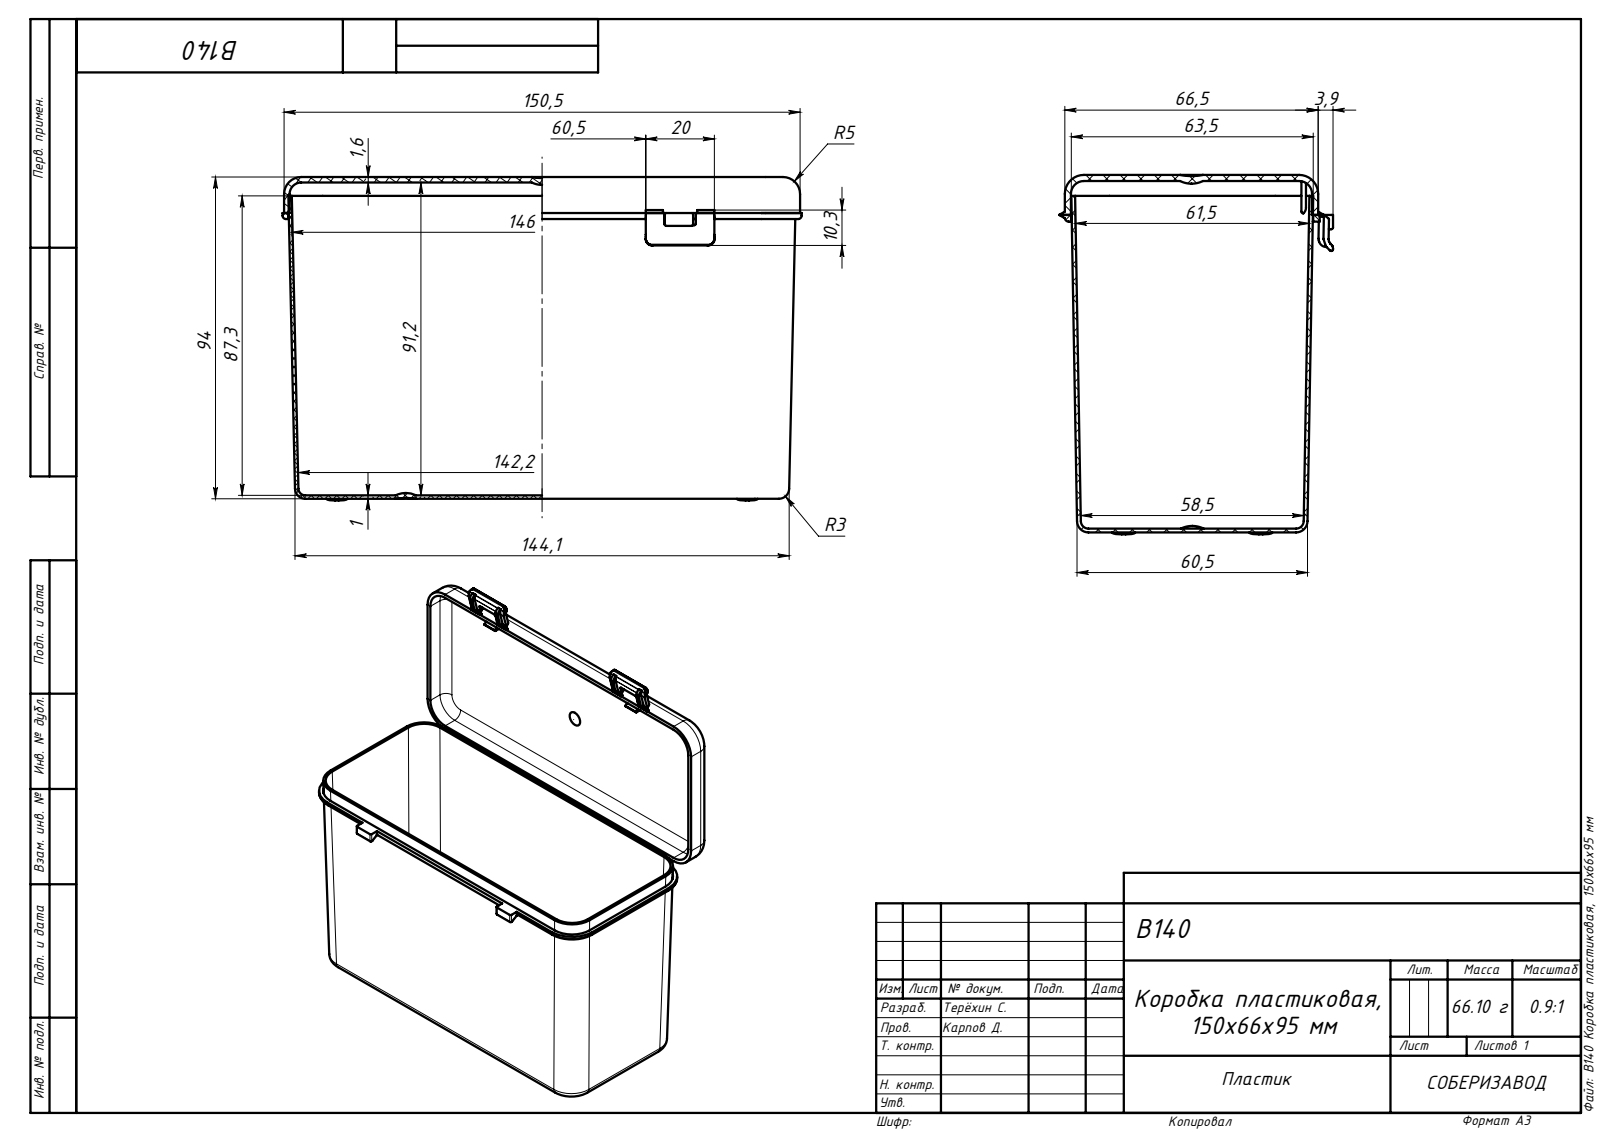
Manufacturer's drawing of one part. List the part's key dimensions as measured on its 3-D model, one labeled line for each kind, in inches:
Part name (STEP PRODUCT): B140 Емкость_00; B140 Защёлка_00; B140 Крышка_12; B140 Коробка пластиковая, 150x66x95 мм
STEP written by: SolidWorks 2019 (AUTOMOTIVE_DESIGN)
Units: inches
Bodies: 13 solids, 324 faces (149 planar, 107 cylindrical, 68 other)
Overall size (bounding box): 5.961 × 3.713 × 2.831
Volume: 3.994 in³ · Surface area: 181.6 in²
Partial cylindrical surfaces — rounded edges, fillets, slot ends (radius × count): R0.02 ×28, R0.079 ×10, R0.394 ×8, R0.039 ×4, R0.118 ×4, R0.134 ×4, R0.197 ×4, R0.331 ×4
Main face-to-face distances: 0.039, 0.063, 3.63, 3.693, 3.591, 3.654, 3.28, 3.24, 0.35, 0.413
